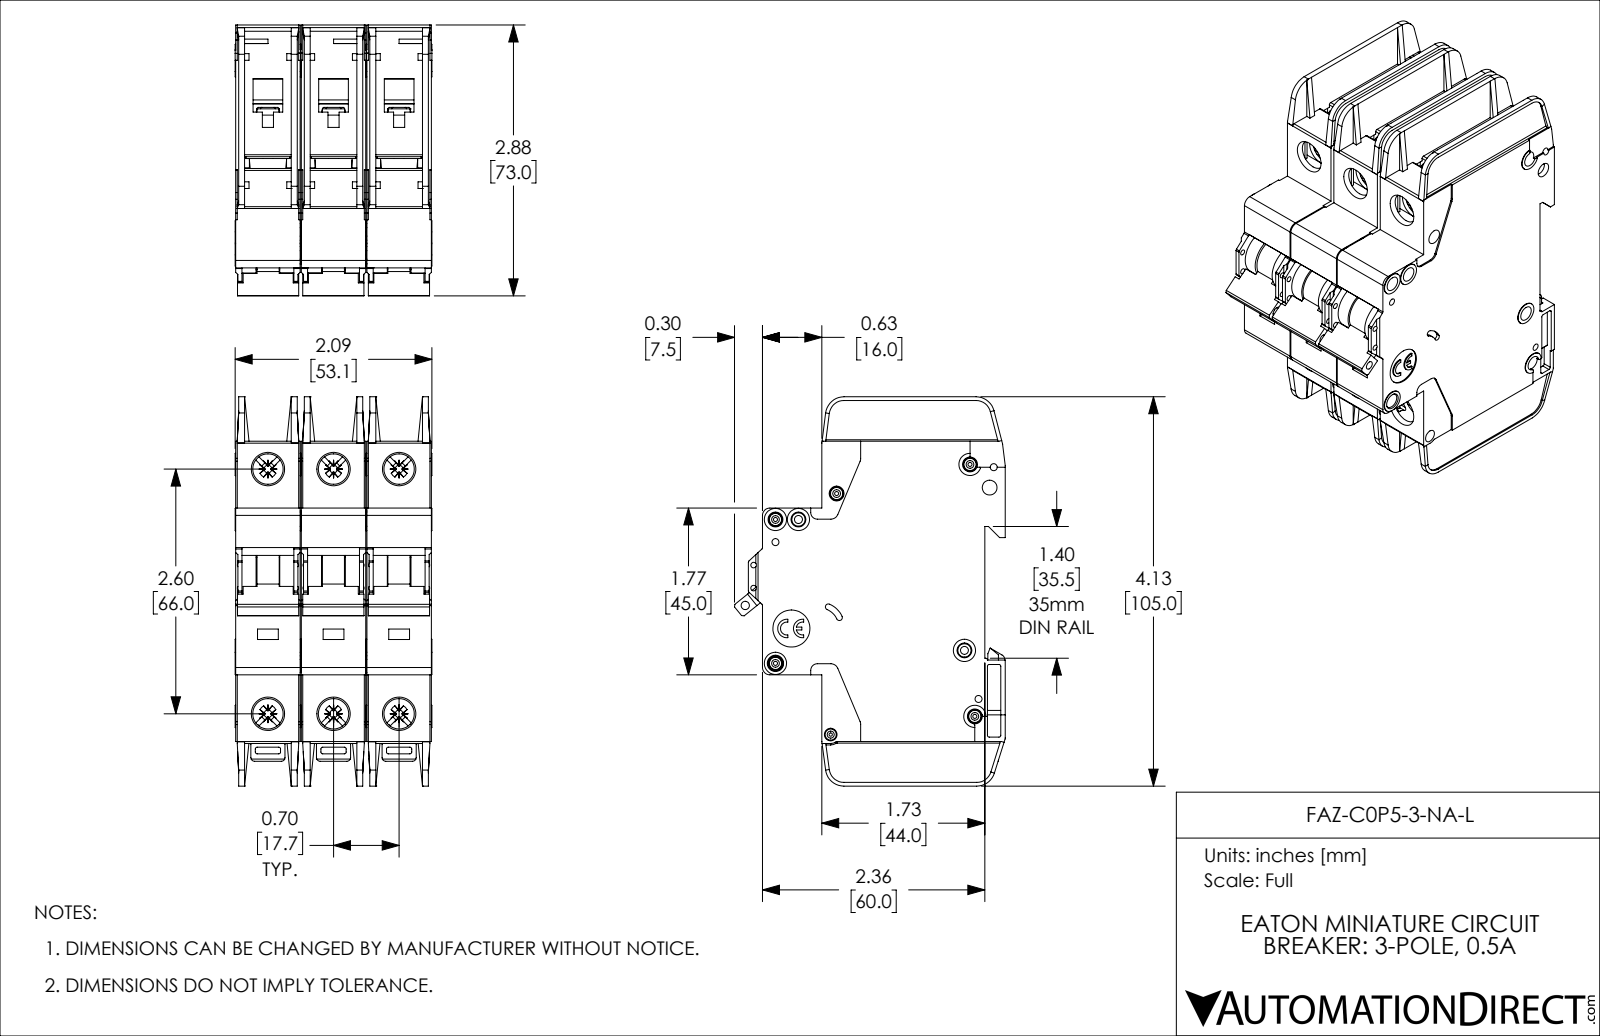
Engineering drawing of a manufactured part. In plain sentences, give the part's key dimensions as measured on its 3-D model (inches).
The part is named "FAZ-C0P5-3-NA-L". Its 3-D file was written by "SolidWorks 2019 (AUTOMOTIVE_DESIGN)". It is 3 solids with 3381 faces: 2013 planar, 1071 cylindrical and 297 other. Overall it measures 4.134 by 2.876 by 2.091 inches. Its volume is 14.05 cubic inches and its surface area 123 square inches. Round holes: 8 of diameter 0.157, 6 of diameter 0.323, 5 of diameter 0.043, 4 of diameter 0.075, 2 of diameter 0.059, 2 of diameter 0.085, 1 of diameter 0.035, 1 of diameter 0.089, 1 of diameter 0.098, 1 of diameter 0.134, 1 of diameter 0.394. Round bosses or shafts: 5 of diameter 0.13, 4 of diameter 0.236, 4 of diameter 0.118, 3 of diameter 0.098. Partial cylindrical surfaces (rounded edges, fillets, slot ends): 72 of radius 0.02, 30 of radius 0.016, 18 of radius 0.039, 12 of radius 0.043, 12 of radius 0.079, 6 of radius 0.008, 6 of radius 0.01, 6 of radius 0.028. The main face-to-face distances are 0.697, 0.047, 1.394, 0.685, 0.591, 1.382, 0.744, 0.65, 0.106, 0.094. The hole center spacings are 0.697, 2.69, 2.598, 0.244, 0.537, 0.87, 1.394, 2.948.
